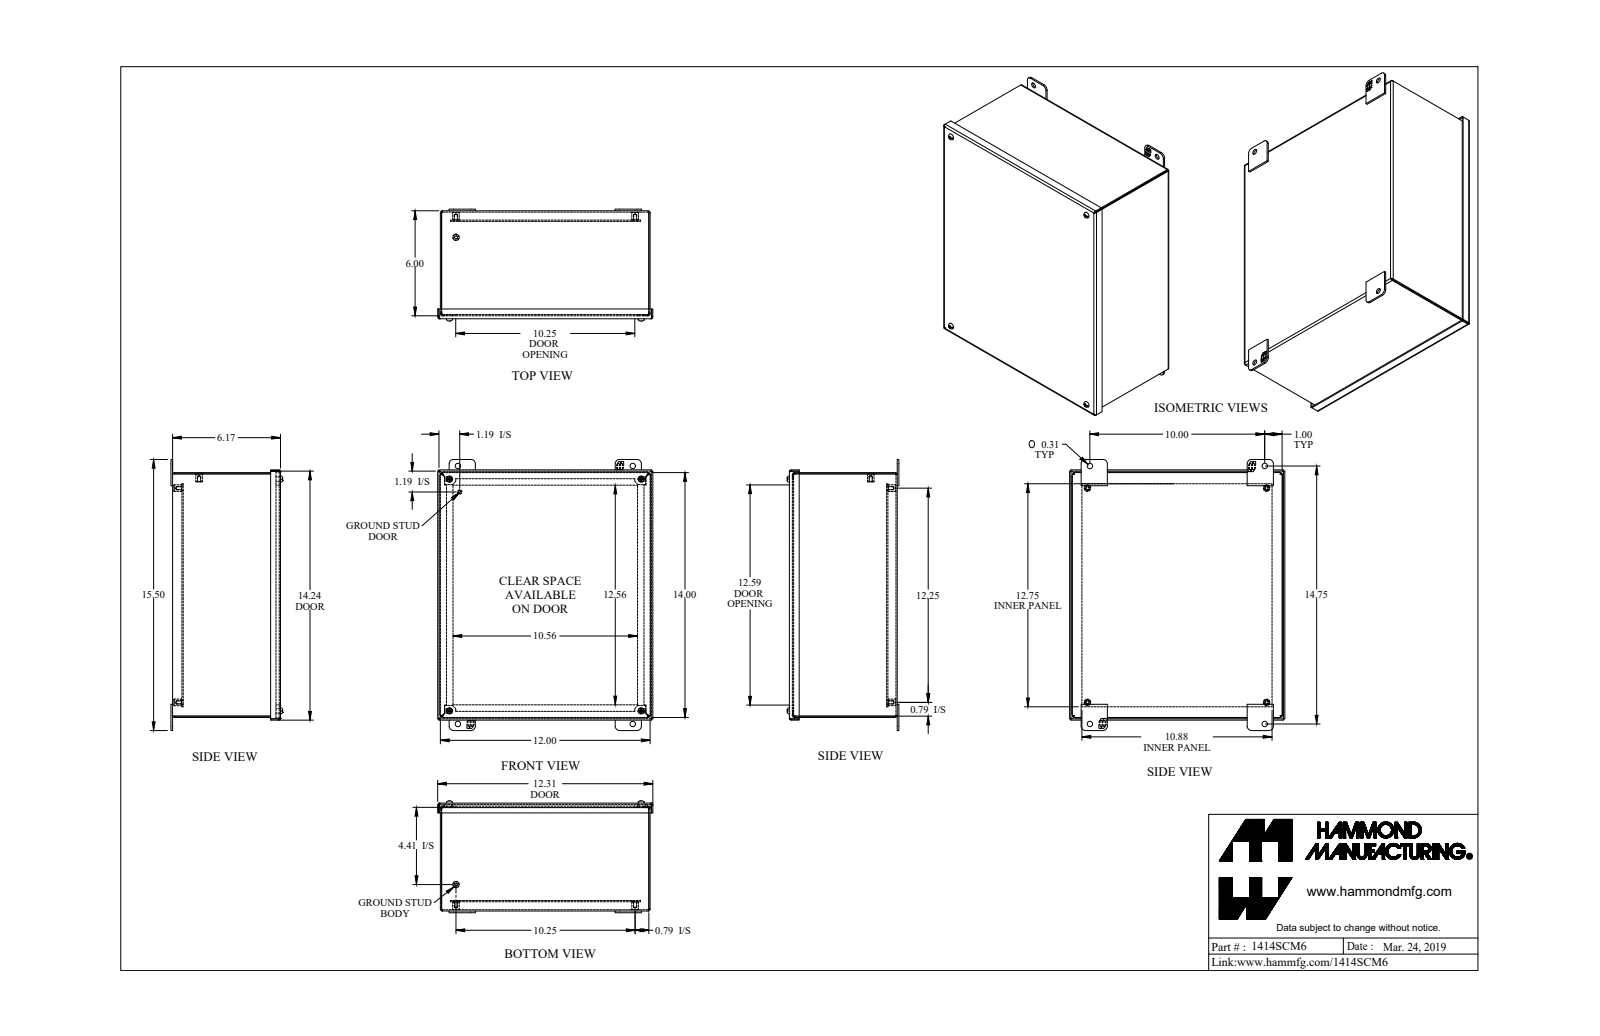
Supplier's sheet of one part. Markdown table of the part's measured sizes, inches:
| quantity | value |
| --- | --- |
| part name | 1414SCM6 |
| STEP written by | SolidWorks 2019 (AUTOMOTIVE_DESIGN) |
| units | inches |
| bodies | 30 solids, 710 faces (478 planar, 172 cylindrical, 60 other) |
| overall size | 15.5 × 12.312 × 6.394 |
| volume | 67.42 in³ |
| surface area | 1 789 in² |
| round holes (diameter × count) | 0.156 × 5, 0.159 × 4, 0.25 × 4, 0.265 × 4, 0.312 × 4 |
| round bosses / shafts (diameter × count) | 0.375 × 5, 0.39 × 4, 0.275 × 4, 0.19 × 4, 0.148 × 4, 0.25 × 1, 0.188 × 1 |
| partial cylindrical surfaces (radius × count) | 0.25 × 12, 0.007 × 8, 0.036 × 8, 0.079 × 8, 0.108 × 8, 0.125 × 8, 0.281 × 8, 0.16 × 4 |
| main face-to-face distances | 0.072, 6.1, 5.568, 0.532, 6.172, 6.028, 11.928, 5.64, 0.46, 5.496 |
| hole center spacings | 10.507, 0.89, 14.009, 17.489, 10, 10.25, 10.956, 10.956 |
